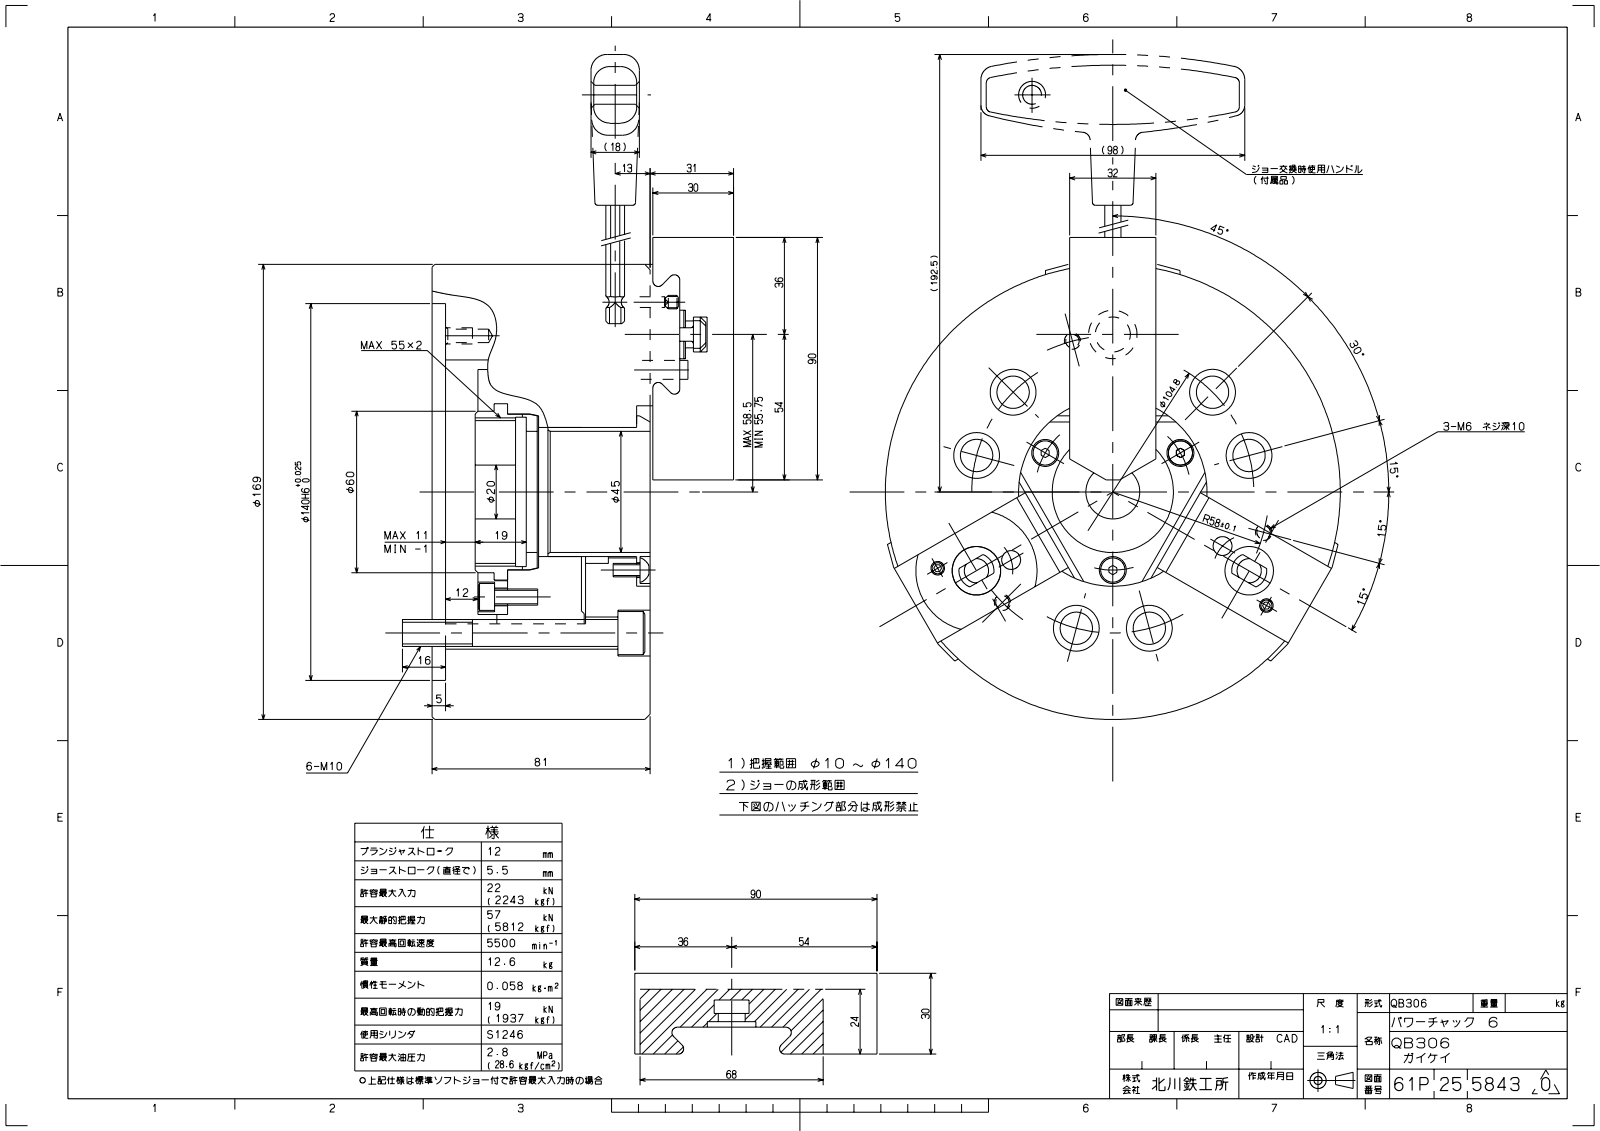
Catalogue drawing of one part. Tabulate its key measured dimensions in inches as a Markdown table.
| quantity | value |
| --- | --- |
| part name | QB306_mid stroke |
| STEP written by | ST-DEVELOPER v16.7 (AUTOMOTIVE_DESIGN) |
| units | inches |
| bodies | 4 solids, 1500 faces (832 planar, 240 cylindrical, 428 other) |
| overall size | 6.903 × 6.784 × 4.843 |
| volume | 104.5 in³ |
| surface area | 396.5 in² |
| round holes (diameter × count) | 0.205 × 18, 0.26 × 9, 0.433 × 9, 0.472 × 6, 0.591 × 6, 0.669 × 6, 0.394 × 4, 0.165 × 3, 0.217 × 3, 0.276 × 3, 0.709 × 3, 0.335 × 1 |
| round bosses / shafts (diameter × count) | 0.19 × 12, 0.335 × 9, 0.63 × 6, 0.383 × 6, 0.374 × 3, 6.654 × 1, 3.571 × 1, 2.579 × 1 |
| partial cylindrical surfaces (radius × count) | 0.197 × 18, 0.016 × 12, 0.079 × 12, 0.236 × 6, 0.433 × 6, 0.984 × 6, 0.247 × 5, 0.256 × 3 |
| main face-to-face distances | 0.197, 3.189, 0.591, 0.394, 0.039, 0.551, 0.276, 1.22, 2.047, 2.992 |
| hole center spacings | 1.535, 0.665, 0.695, 1.26, 1.87, 1.924, 1.992, 2.537 |
